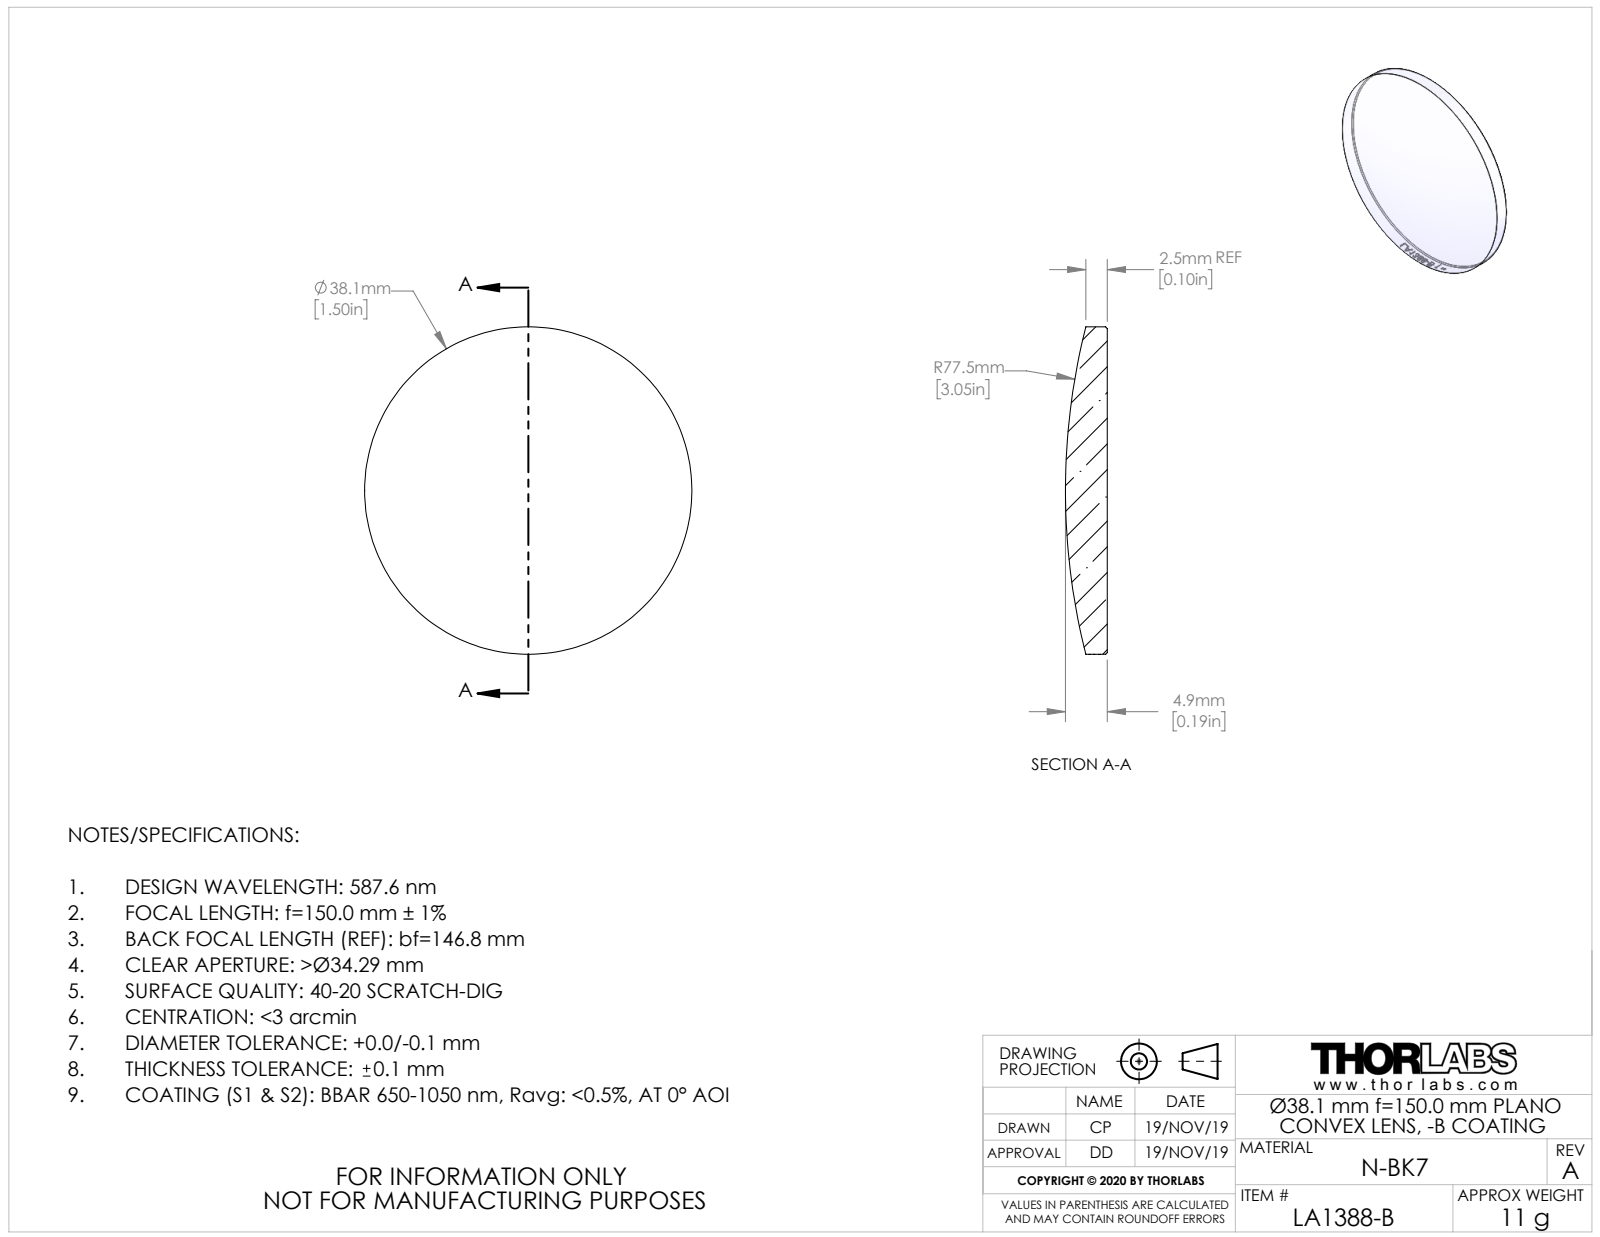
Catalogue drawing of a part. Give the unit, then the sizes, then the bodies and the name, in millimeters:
Units: millimetres
Overall size (bounding box): 38.1 × 38.1 × 4.88
Round bosses / shafts (diameter × count): ⌀38.1 ×1
Volume: 4 213 mm³ · Surface area: 2 583 mm²
Bodies: 1 solid, 26 faces (1 planar, 21 cylindrical, 4 other)
Part name (STEP PRODUCT): TTN200729-E0W
STEP written by: SolidWorks 2018 (CONFIG_CONTROL_DESIGN)
